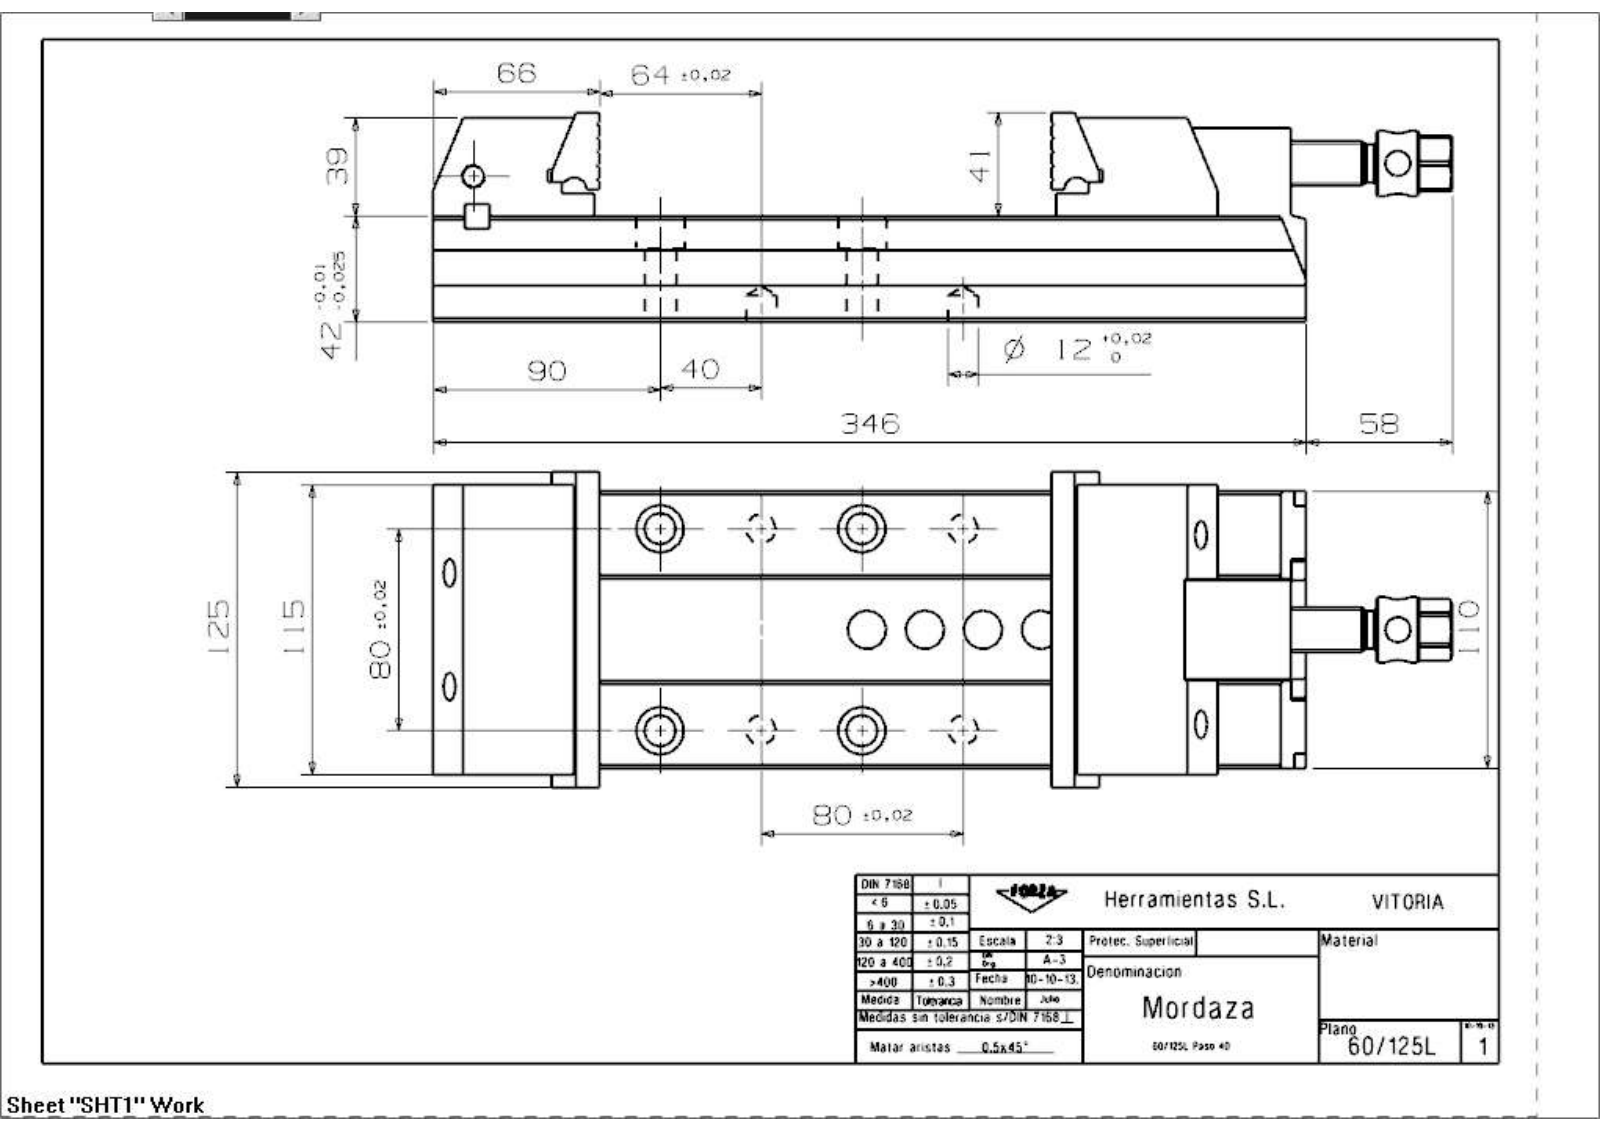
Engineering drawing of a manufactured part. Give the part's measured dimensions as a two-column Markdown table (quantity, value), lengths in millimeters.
| quantity | value |
| --- | --- |
| part name | 60_125_Mordaza |
| STEP written by | SIEMENS PLM Software NX 7.5 (CONFIG_CONTROL_DESIGN) |
| units | millimeters |
| bodies | 10 solids, 402 faces (239 planar, 117 cylindrical, 46 other) |
| overall size | 358 × 125 × 83 |
| volume | 1 502 000 mm³ |
| surface area | 267 497 mm² |
| round holes (diameter × count) | 7.5 × 4, 11.5 × 4, 12 × 4, 12.5 × 4, 19 × 4, 8.78 × 3, 5.19 × 2, 6.5 × 2, 6.99 × 2, 8 × 2, 10 × 2, 12.38 × 2 |
| round bosses / shafts (diameter × count) | 26 × 1, 17.73 × 1, 15 × 1, 14.5 × 1, 10.5 × 1 |
| partial cylindrical surfaces (radius × count) | 0.3 × 20, 10 × 4, 16 × 4, 6 × 3, 1.6 × 2, 5 × 2, 3 × 1, 8 × 1 |
| main face-to-face distances | 42, 15.4, 8.5, 26.6, 27, 39, 29.5, 77, 81, 65.6 |
| hole center spacings | 80, 40, 89.44, 113.14, 9.19, 15, 23.07, 23.76 |
